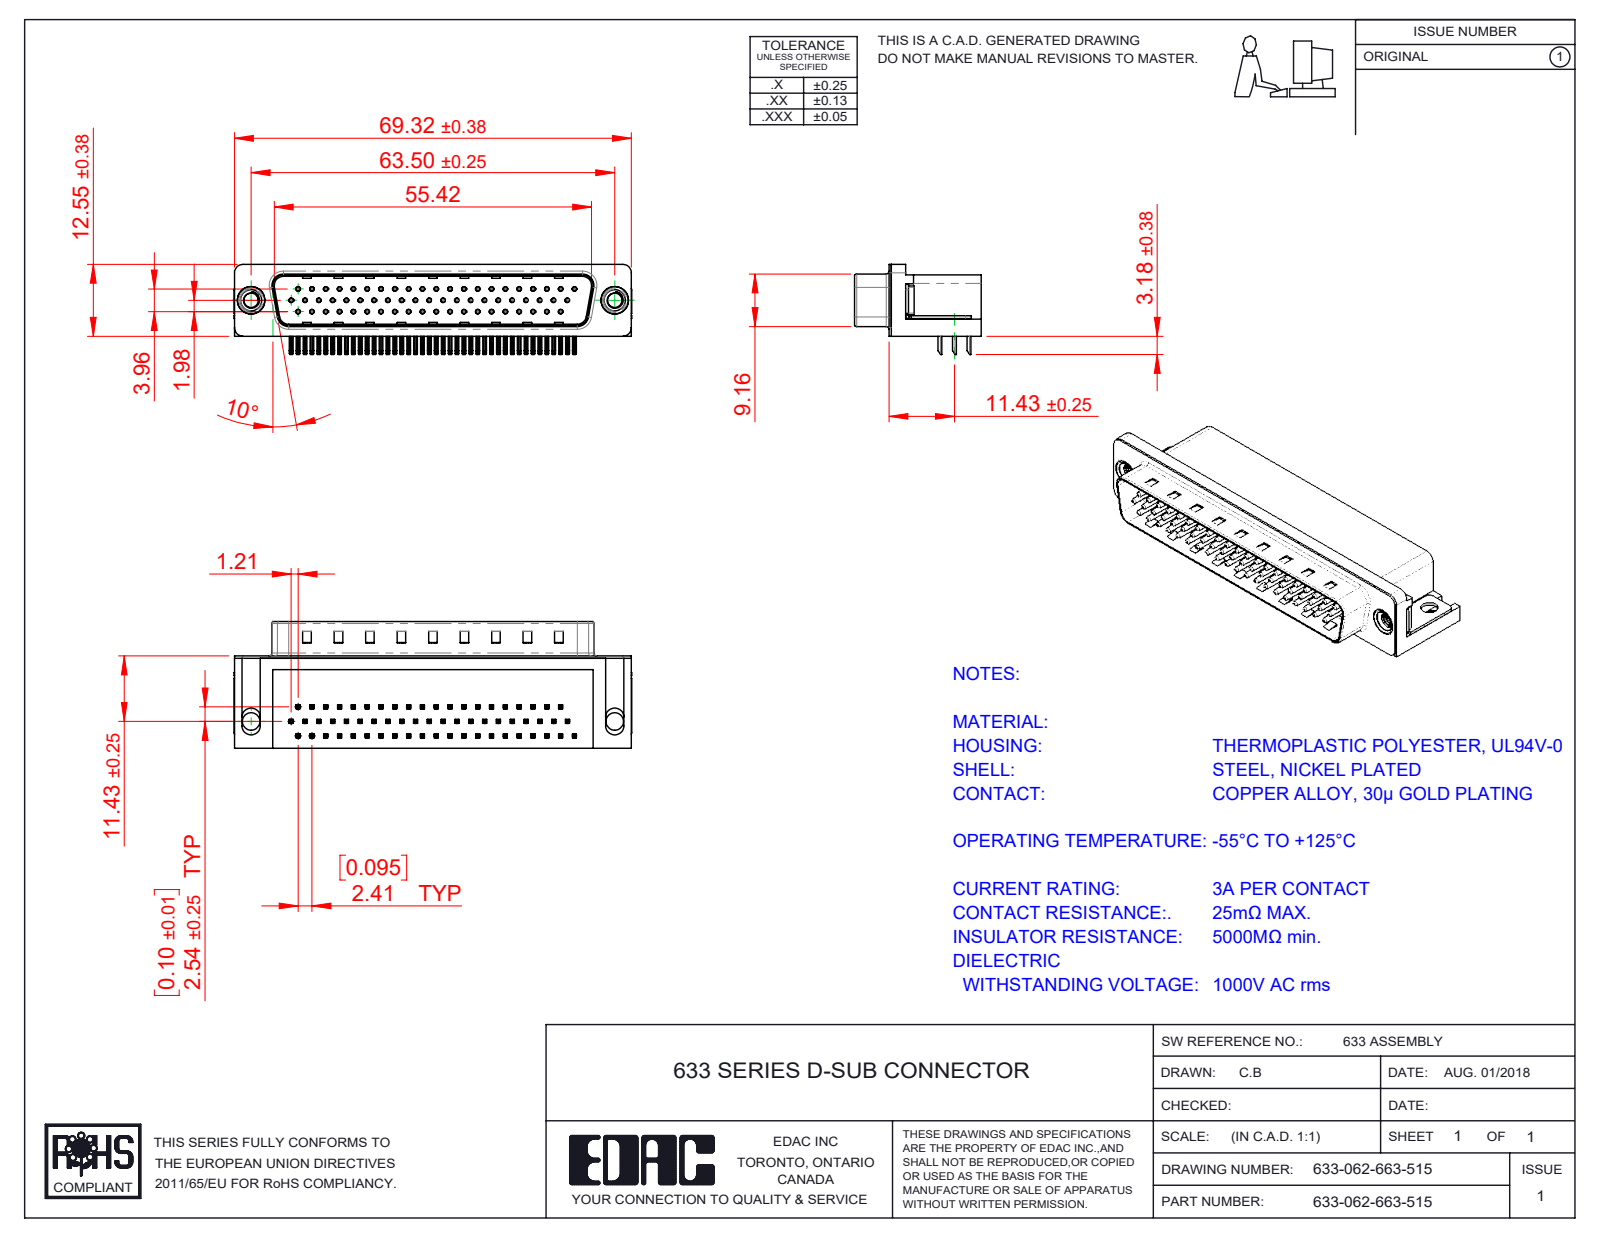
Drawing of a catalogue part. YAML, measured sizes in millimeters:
part_name: "633-062-663-515; 633 Thru Hole Board Mount; 633 Housing_62 Contact; 633 Contact Bottom (+4 more)"
step_written_by: "SolidWorks 2016 (CONFIG_CONTROL_DESIGN)"
units: millimeters
bodies: {solids: 68, faces: 5074, planar: 3211, cylindrical: 1446, other: 417}
overall_size: [69.4, 22.1, 15.73]
volume: 11048
surface_area: 13396
round_holes:
  - {diameter: 0.35, count: 62}
  - {diameter: 0.8, count: 62}
  - {diameter: 2.5, count: 2}
  - {diameter: 3.05, count: 2}
  - {diameter: 4, count: 2}
  - {diameter: 4.8, count: 2}
  - {diameter: 5, count: 2}
round_bosses_or_shafts:
  - {diameter: 0.75, count: 62}
  - {diameter: 4.9, count: 2}
  - {diameter: 4.75, count: 2}
  - {diameter: 3.9, count: 2}
partial_cylinders:
  - {radius: 0.25, count: 256}
  - {radius: 0.12, count: 124}
  - {radius: 1, count: 16}
  - {radius: 0.5, count: 9}
  - {radius: 1.6, count: 8}
  - {radius: 1.5, count: 7}
  - {radius: 0.9, count: 4}
  - {radius: 2, count: 4}
face_to_face_distances: [0.4, 10.35, 15.7, 8.76, 2.9, 2.5, 2.54, 8.36, 2.1, 16.1]
hole_center_spacings: [2.41, 4.82, 7.24, 9.65, 14.48, 16.89, 4.83, 7.23]
